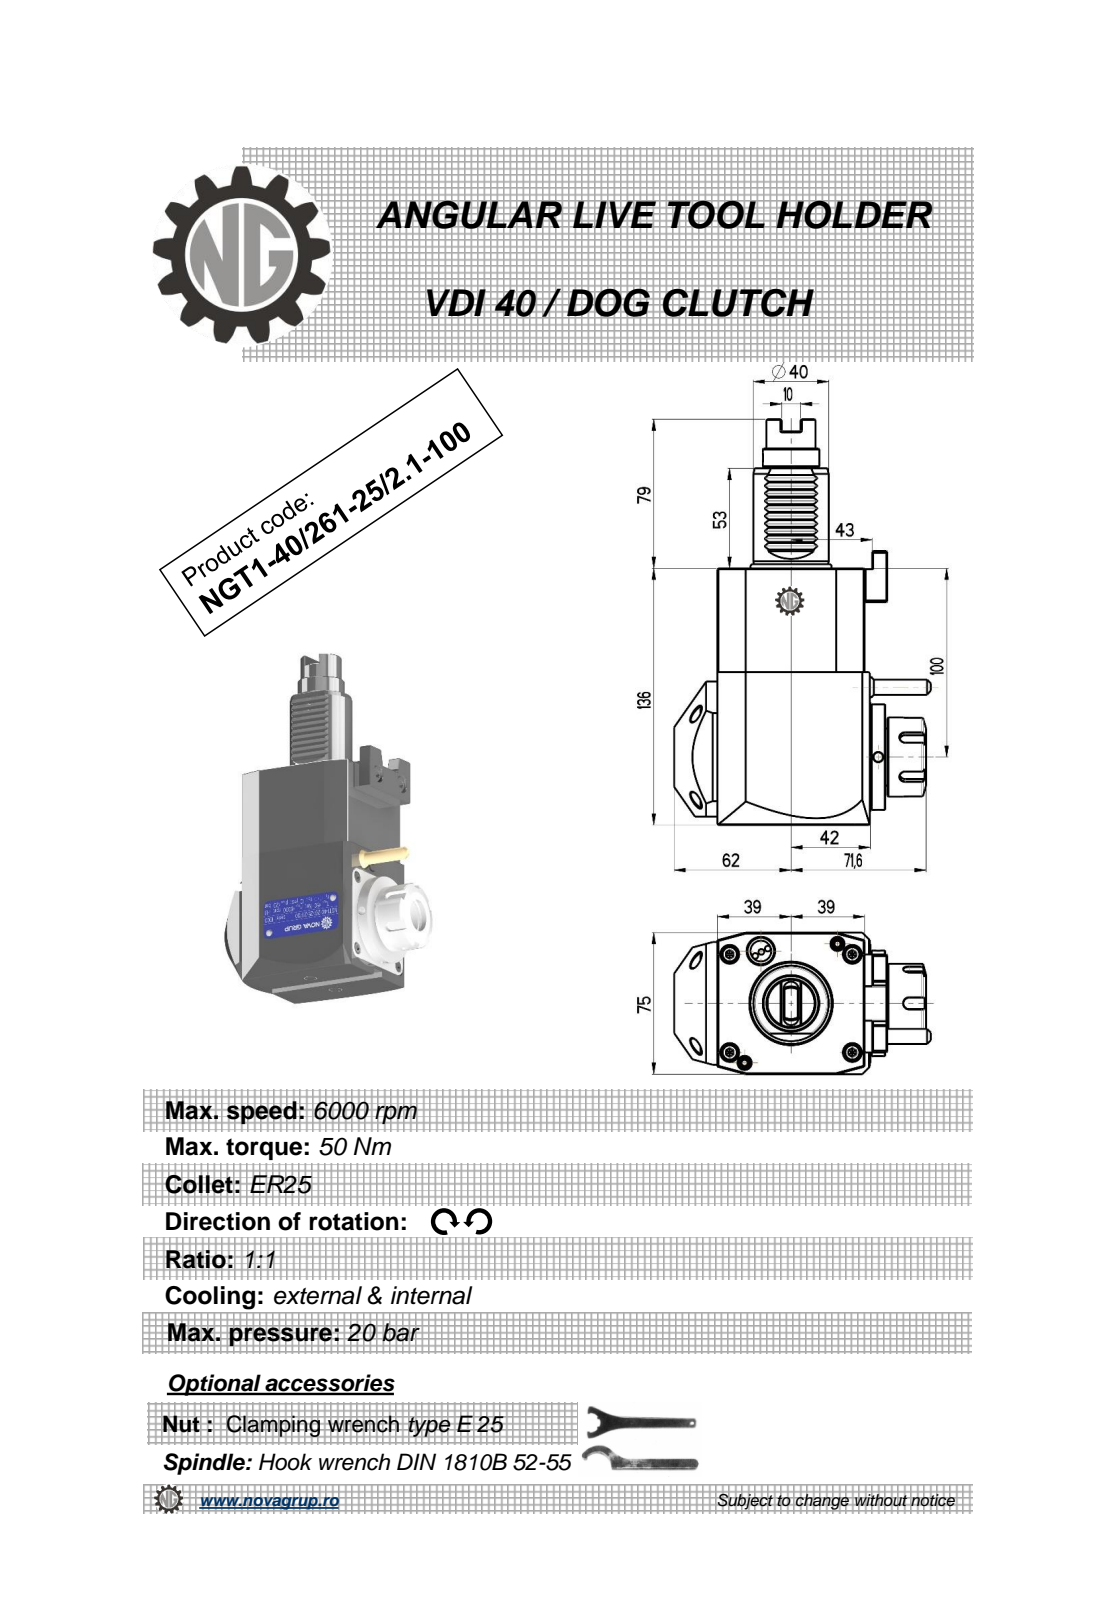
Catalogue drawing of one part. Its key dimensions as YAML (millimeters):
part_name: "NGT1_40_261_25_2_1_100"
step_written_by: "PRO/ENGINEER BY PARAMETRIC TECHNOLOGY CORPORATION, 2010280 (CONFIG_CONTROL_DESIGN)"
units: millimeters
bodies: {solids: 1, faces: 387, planar: 192, cylindrical: 68, other: 127}
overall_size: [215, 136.14, 75]
volume: 999020
surface_area: 76884
round_holes:
  - {diameter: 5, count: 3}
  - {diameter: 3, count: 1}
  - {diameter: 4.2, count: 1}
  - {diameter: 20.3, count: 1}
round_bosses_or_shafts:
  - {diameter: 56, count: 1}
  - {diameter: 43, count: 1}
  - {diameter: 42, count: 1}
  - {diameter: 40, count: 1}
  - {diameter: 33, count: 1}
  - {diameter: 30, count: 1}
  - {diameter: 26, count: 1}
  - {diameter: 11.2, count: 1}
partial_cylinders:
  - {radius: 0.3, count: 10}
  - {radius: 0.22, count: 6}
  - {radius: 3, count: 5}
  - {radius: 0.5, count: 3}
  - {radius: 1, count: 2}
  - {radius: 12.5, count: 1}
  - {radius: 40, count: 1}
face_to_face_distances: [75, 136, 78, 81, 0.5, 3, 8, 11, 84.88, 8.2]
hole_center_spacings: [40.93, 122.75, 158.5]
